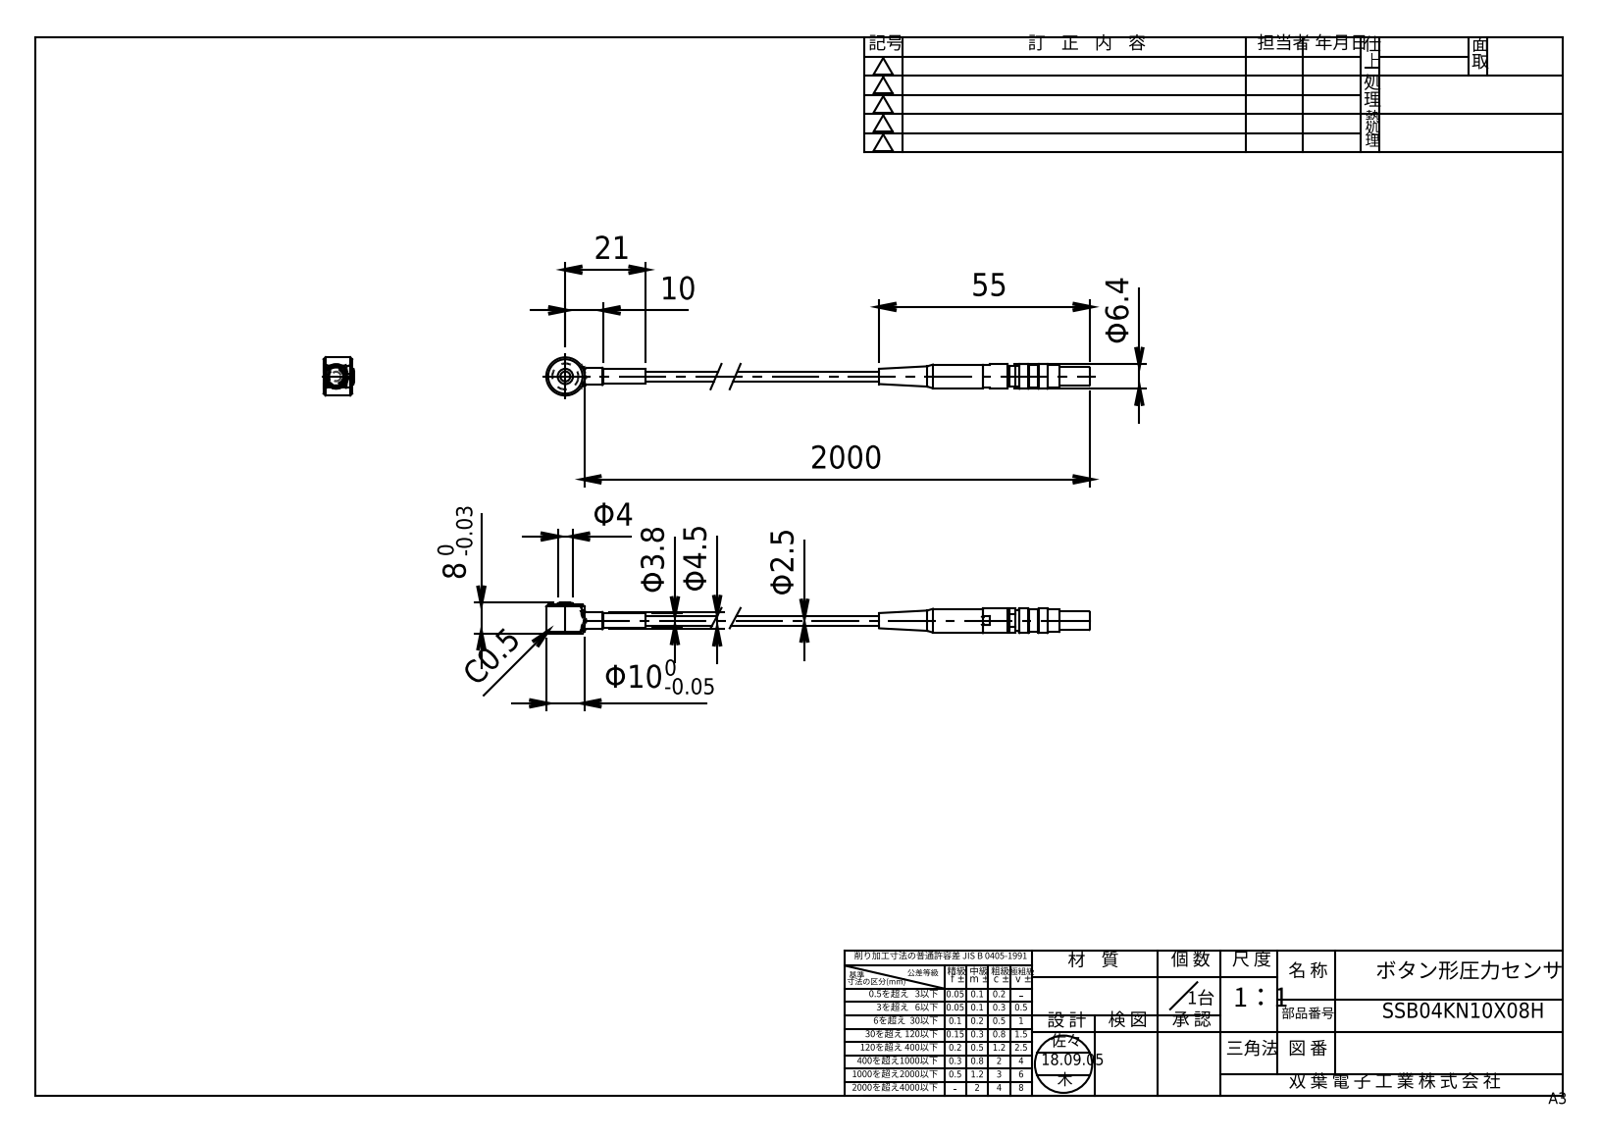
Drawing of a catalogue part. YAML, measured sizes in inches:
step_written_by: "XStep 1.0 (automotive_design)"
units: inches
bodies: {solids: 1, faces: 76, planar: 30, cylindrical: 21, other: 25}
overall_size: [79.134, 0.394, 0.315]
volume: 0.712
surface_area: 26.02
round_holes:
  - {diameter: 0.268, count: 1}
round_bosses_or_shafts:
  - {diameter: 0.252, count: 1}
  - {diameter: 0.25, count: 1}
  - {diameter: 0.244, count: 1}
  - {diameter: 0.236, count: 1}
  - {diameter: 0.211, count: 1}
  - {diameter: 0.197, count: 1}
  - {diameter: 0.195, count: 1}
  - {diameter: 0.177, count: 1}
partial_cylinders:
  - {radius: 0.083, count: 2}
  - {radius: 0.197, count: 1}
  - {radius: 0.199, count: 1}
face_to_face_distances: [0.291, 0.295, 0.315, 0.849, 0.098, 0.022, 0.827, 0.226, 78.11, 0.085]
